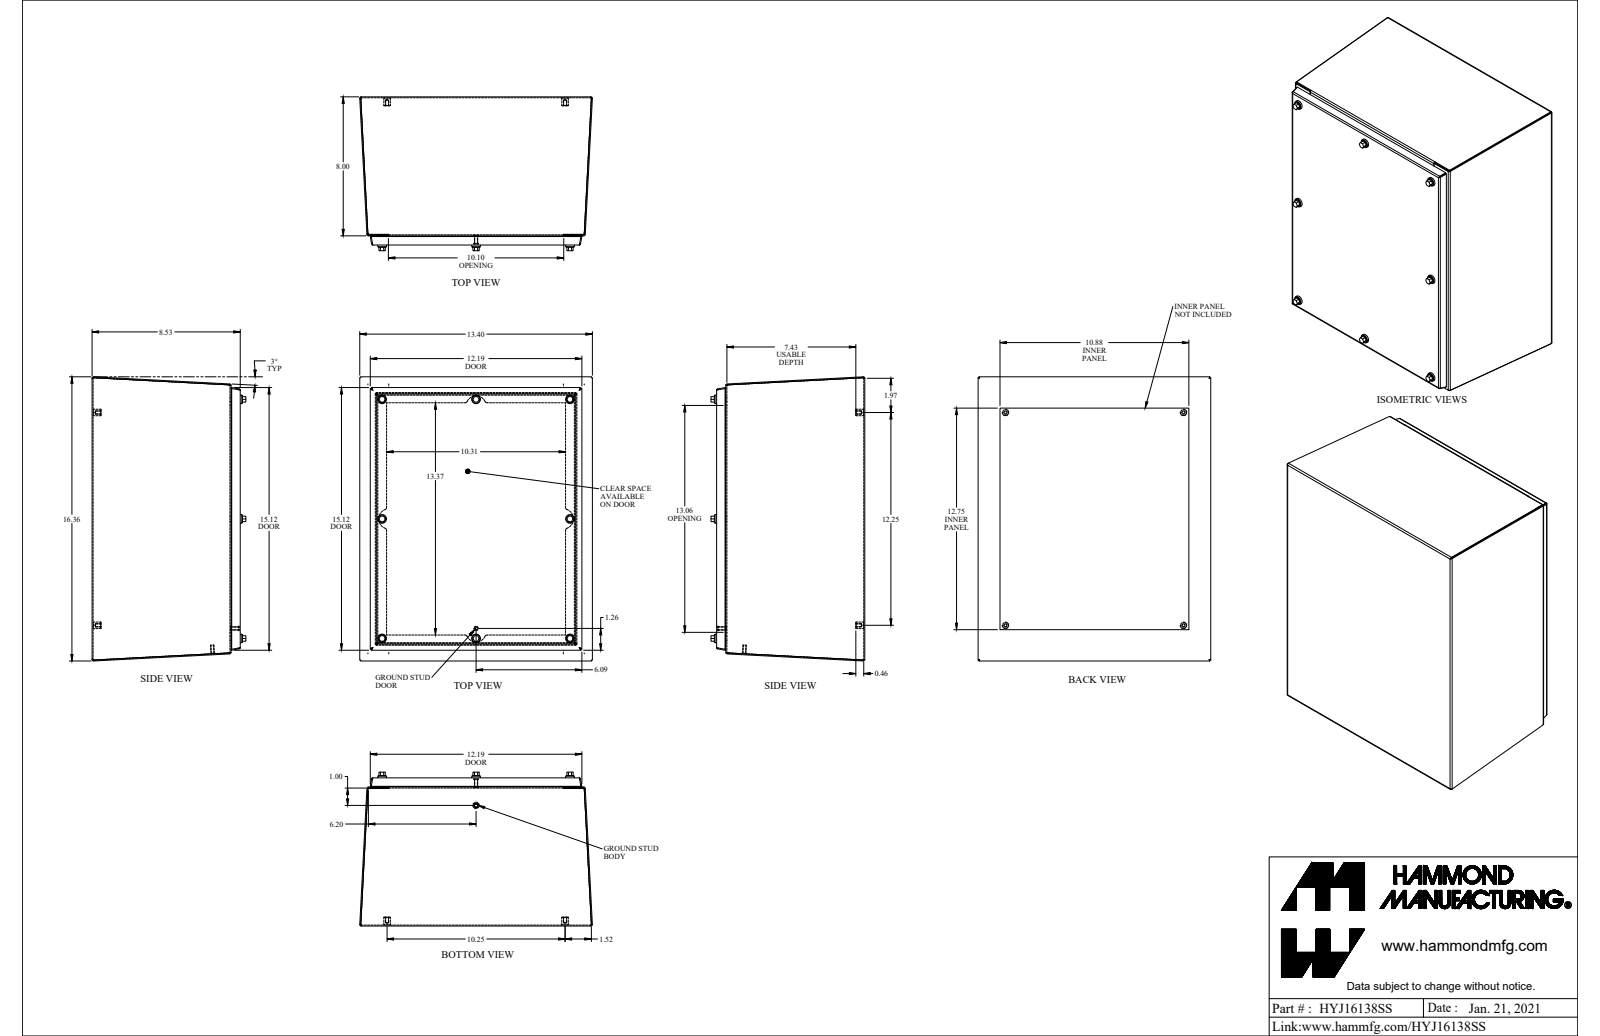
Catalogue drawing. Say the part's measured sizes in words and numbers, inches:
The part is named "HYJ16138SS". Its 3-D file was written by "SolidWorks 2021 (AUTOMOTIVE_DESIGN)". It is 42 solids with 657 faces: 417 planar, 204 cylindrical and 36 other. Overall it measures 16.36 by 13.396 by 8.859 inches. Its volume is 63.92 cubic inches and its surface area 2 125 square inches. Round holes: 8 of diameter 0.065, 8 of diameter 0.235, 8 of diameter 0.239, 8 of diameter 0.24, 8 of diameter 0.25, 8 of diameter 0.253, 4 of diameter 0.156, 4 of diameter 0.4. Round bosses or shafts: 12 of diameter 0.375, 10 of diameter 0.19, 8 of diameter 0.5, 8 of diameter 0.45, 8 of diameter 0.406, 8 of diameter 0.315, 2 of diameter 0.25. Partial cylindrical surfaces (rounded edges, fillets, slot ends): 16 of radius 0.029, 16 of radius 0.086, 8 of radius 0.076, 8 of radius 0.125, 4 of radius 0.055, 4 of radius 0.5, 4 of radius 0.575. The main face-to-face distances are 0.057, 0.057, 8.475, 8.418, 8.532, 8.475, 7.943, 0.532, 0.475, 8. The hole center spacings are 6.882, 13.764, 0.809, 12.822, 13.01, 14.789, 8.754, 17.507.
